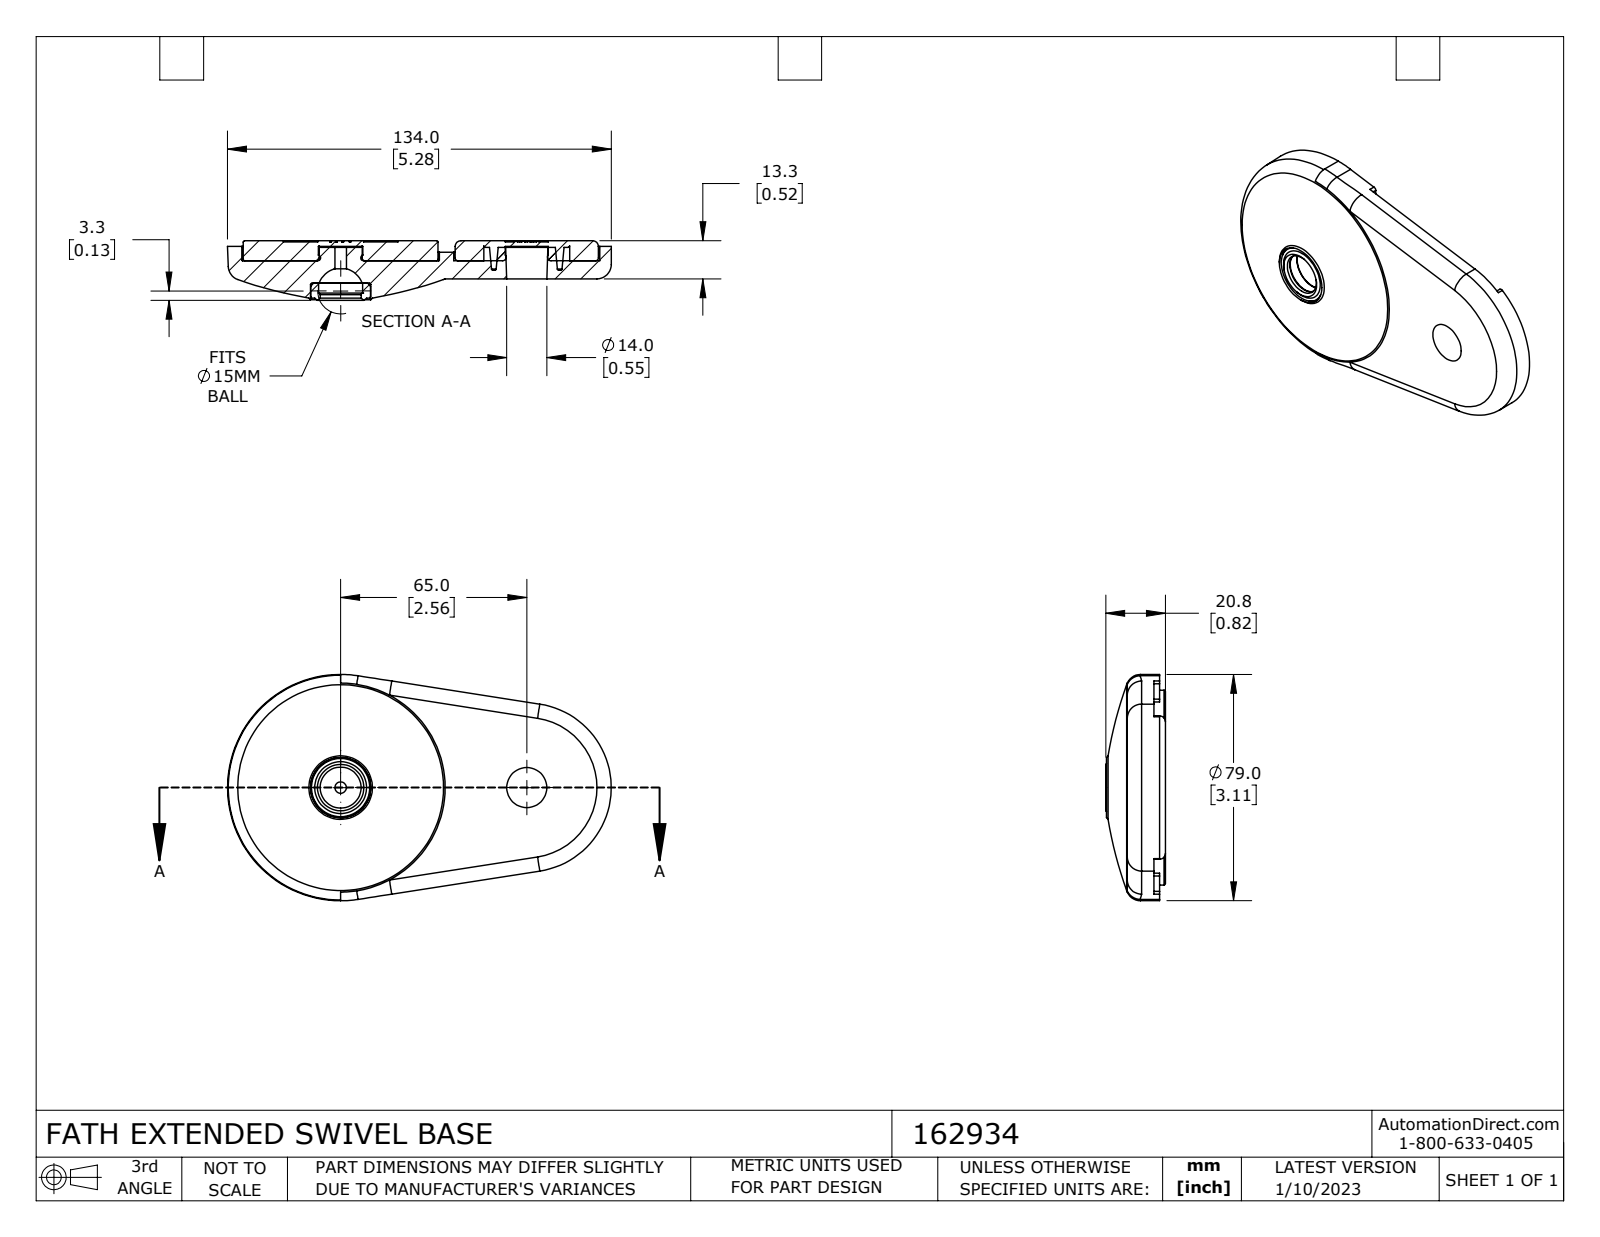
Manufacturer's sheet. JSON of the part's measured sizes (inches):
{"part_name": "162934", "step_written_by": "SolidWorks 2021 (CONFIG_CONTROL_DESIGN)", "units": "inches", "bodies": {"solids": 4, "faces": 266, "planar": 45, "cylindrical": 90, "other": 131}, "overall_size": [5.276, 3.11, 0.819], "volume_in3": 6.548, "surface_area_in2": 61.88, "round_holes": [[0.157, 1], [0.563, 1], [0.591, 1], [0.606, 1], [0.61, 1], [0.827, 1], [1.575, 1], [2.008, 1], [2.717, 1]], "round_bosses_or_shafts": [[2.677, 1], [1.969, 1], [1.181, 1], [0.823, 1], [0.63, 1], [0.591, 1]], "partial_cylinders_radius": [[0.012, 24], [0.039, 14], [0.079, 2], [0.197, 2], [1.122, 1], [1.161, 1], [1.476, 1], [1.555, 1]], "face_to_face_distances": [0.276, 0.248, 0.524, 0.079, 0.118, 0.197, 0.445, 0.016, 0.063, 0.26], "hole_center_spacings": [2.559]}
